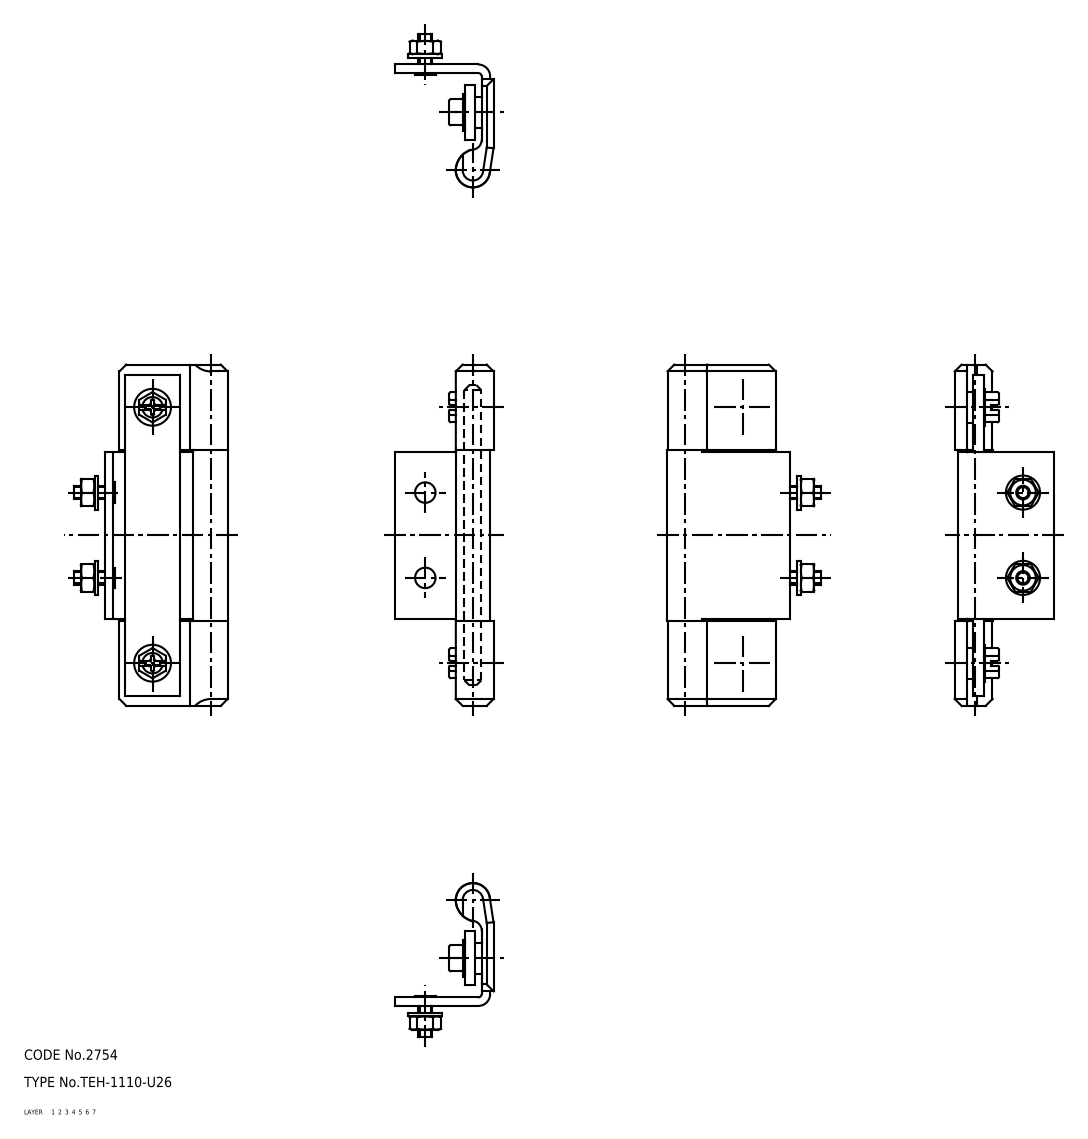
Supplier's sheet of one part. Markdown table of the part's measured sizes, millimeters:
| quantity | value |
| --- | --- |
| part name | hinge pieces_B_mr; washer; nut; screw (+5 more) |
| STEP written by | CADfix (AUTOMOTIVE_DESIGN) |
| units | millimeters |
| bodies | 11 solids, 344 faces (0 planar, 0 cylindrical, 344 other) |
| overall size | 100 × 45.05 × 29 |
| volume | 24 000 mm³ |
| surface area | 20 253 mm² |
